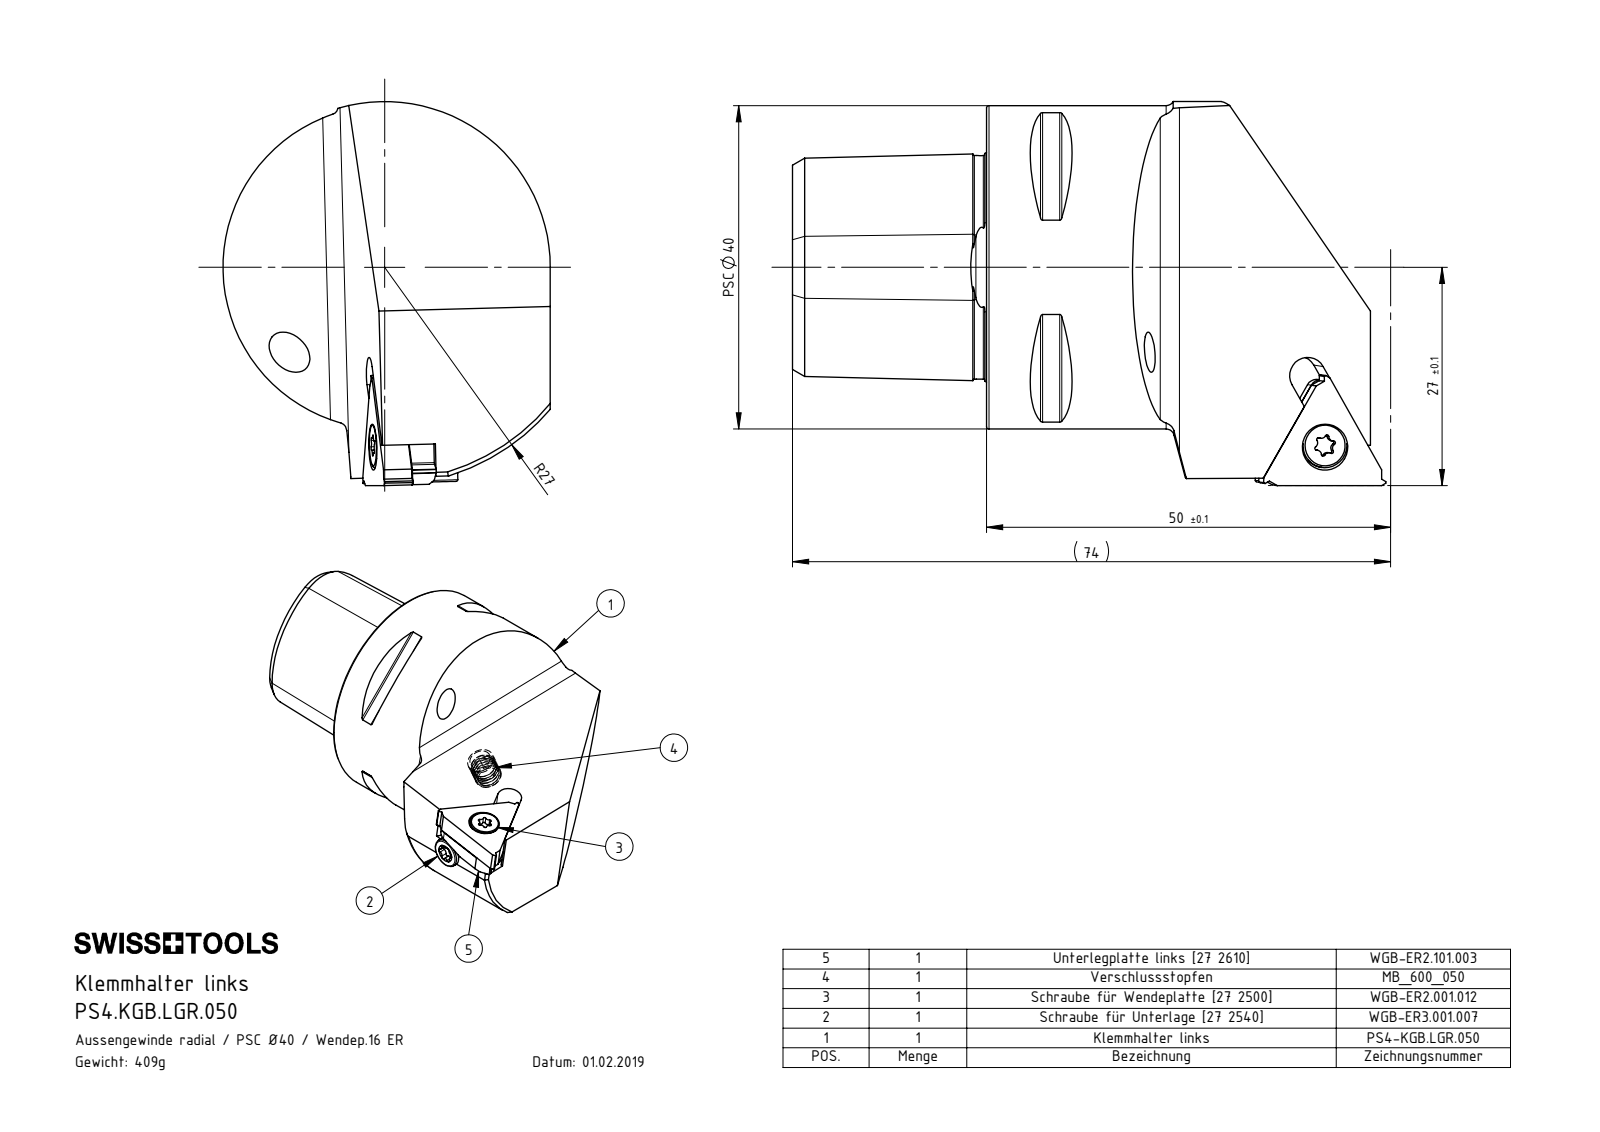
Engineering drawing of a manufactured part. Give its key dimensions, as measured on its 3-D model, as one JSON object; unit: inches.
{"part_name": "LT16EL; WGB-ER2.101.003_A; PS4.KGB.LGR.050; KVT_MB_600_050 (+3 more)", "step_written_by": "SolidWorks 2017 (AUTOMOTIVE_DESIGN)", "units": "inches", "bodies": {"solids": 7, "faces": 247, "planar": 89, "cylindrical": 67, "other": 91}, "overall_size": [2.89, 1.87, 1.594], "volume_in3": 3.155, "surface_area_in2": 21.08, "round_holes": [[0.157, 3], [0.102, 2], [0.165, 2], [0.158, 1], [0.181, 1], [0.197, 1], [0.492, 1], [0.709, 1], [0.787, 1]], "round_bosses_or_shafts": [[0.217, 2], [1.575, 1], [0.197, 1], [0.125, 1], [0.118, 1], [0.109, 1]], "partial_cylinders_radius": [[0.012, 8], [0.009, 6], [0.013, 6], [0.022, 6], [0.022, 6], [0.004, 2], [0.01, 2], [0.118, 2]], "face_to_face_distances": [0.136, 0.126, 0.945, 0.262, 0.611, 0.27, 0.144, 1.39, 0.591, 0.354], "hole_center_spacings": [0.925]}
